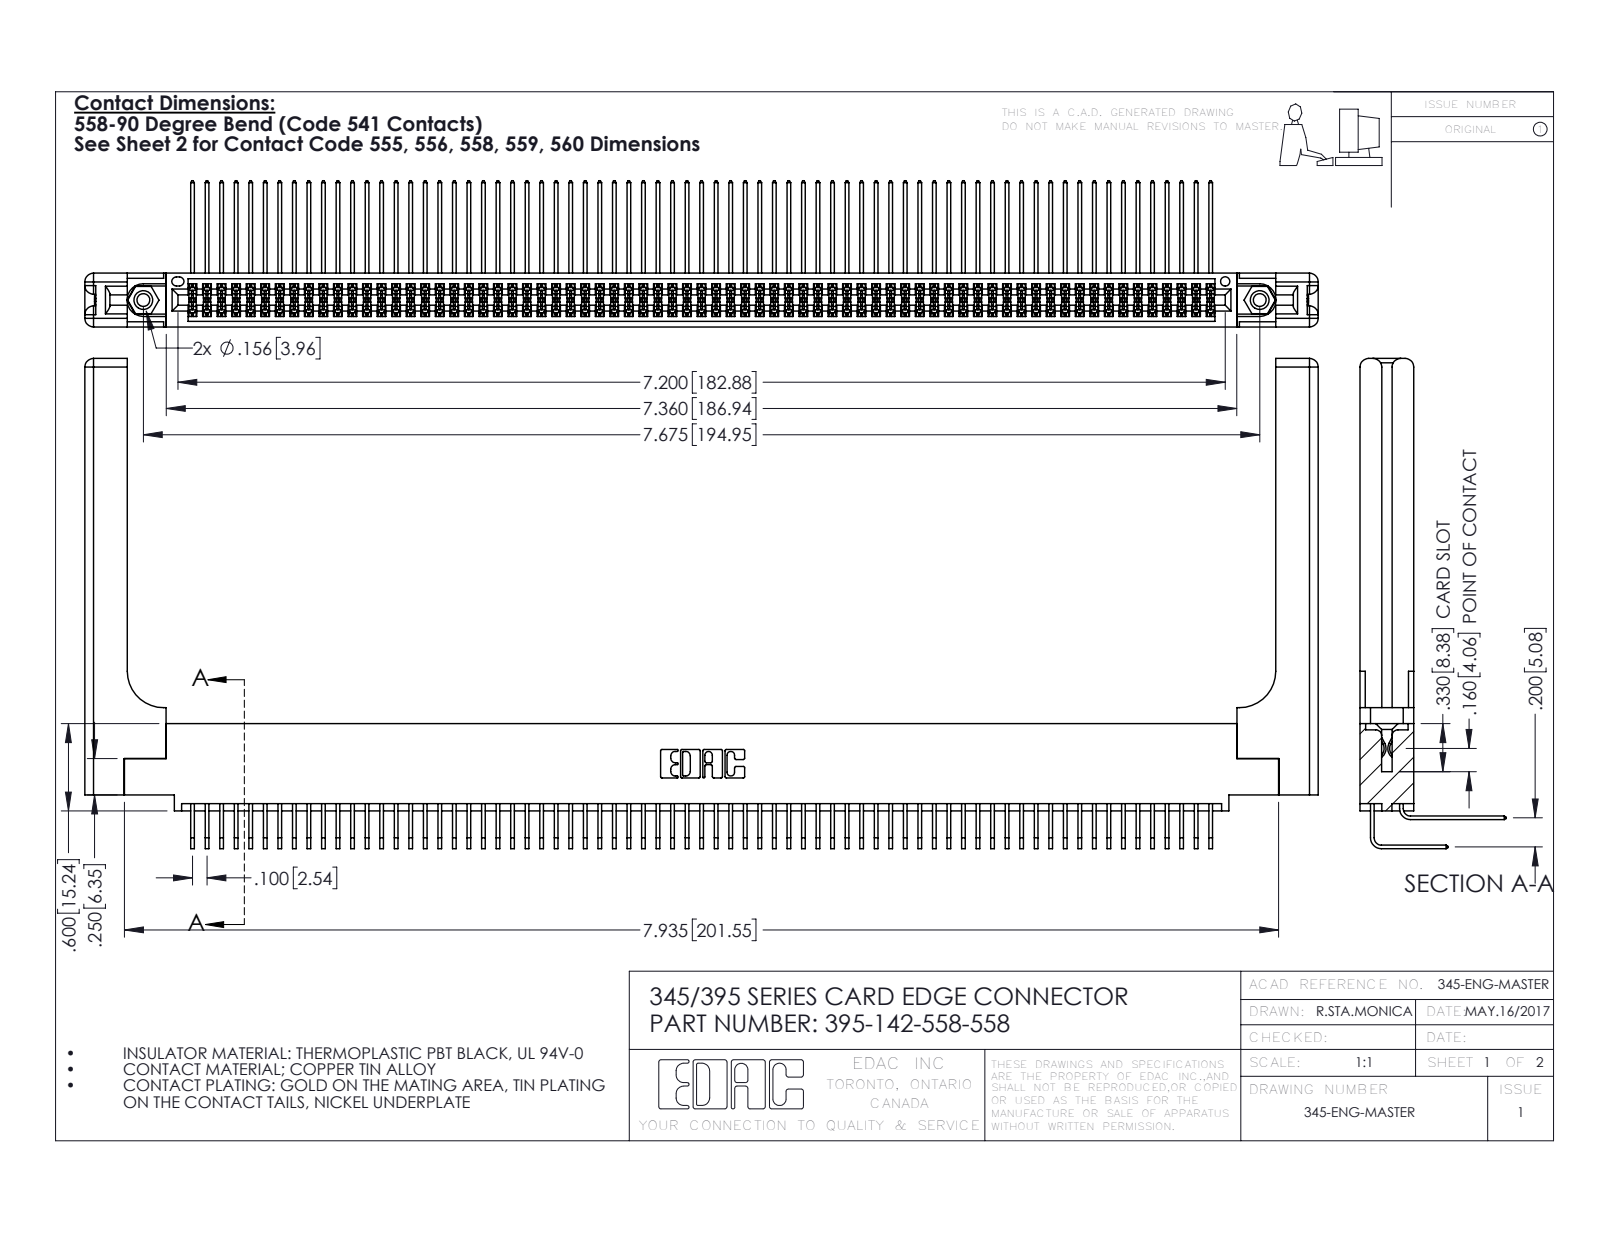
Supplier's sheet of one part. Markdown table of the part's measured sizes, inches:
| quantity | value |
| --- | --- |
| part name | 395-142-558-558; 345-220-058_345-220-058; 345-292-001_558 Tail - 2; 345-292-001_558 559 Tail - 1 (+2 more) |
| STEP written by | SolidWorks 2016 (CONFIG_CONTROL_DESIGN) |
| units | inches |
| bodies | 147 solids, 7770 faces (5202 planar, 2508 cylindrical, 60 other) |
| overall size | 8.479 × 3.369 × 1.005 |
| volume | 1.856 in³ |
| surface area | 65.09 in² |
| round holes (diameter × count) | 0.089 × 2, 0.125 × 2, 0.156 × 2, 0.064 × 1 |
| round bosses / shafts (diameter × count) | 0.155 × 2 |
| partial cylindrical surfaces (radius × count) | 0.006 × 283, 0.01 × 22, 0.06 × 16, 0.007 × 6, 0.031 × 6, 0.026 × 3, 0.014 × 2, 0.019 × 2 |
| main face-to-face distances | 0.072, 0.298, 0.37, 0.2, 0.098, 0.272, 0.025, 0.225, 0.025, 0.175 |
| hole center spacings | 0.27, 7.439, 7.675 |
